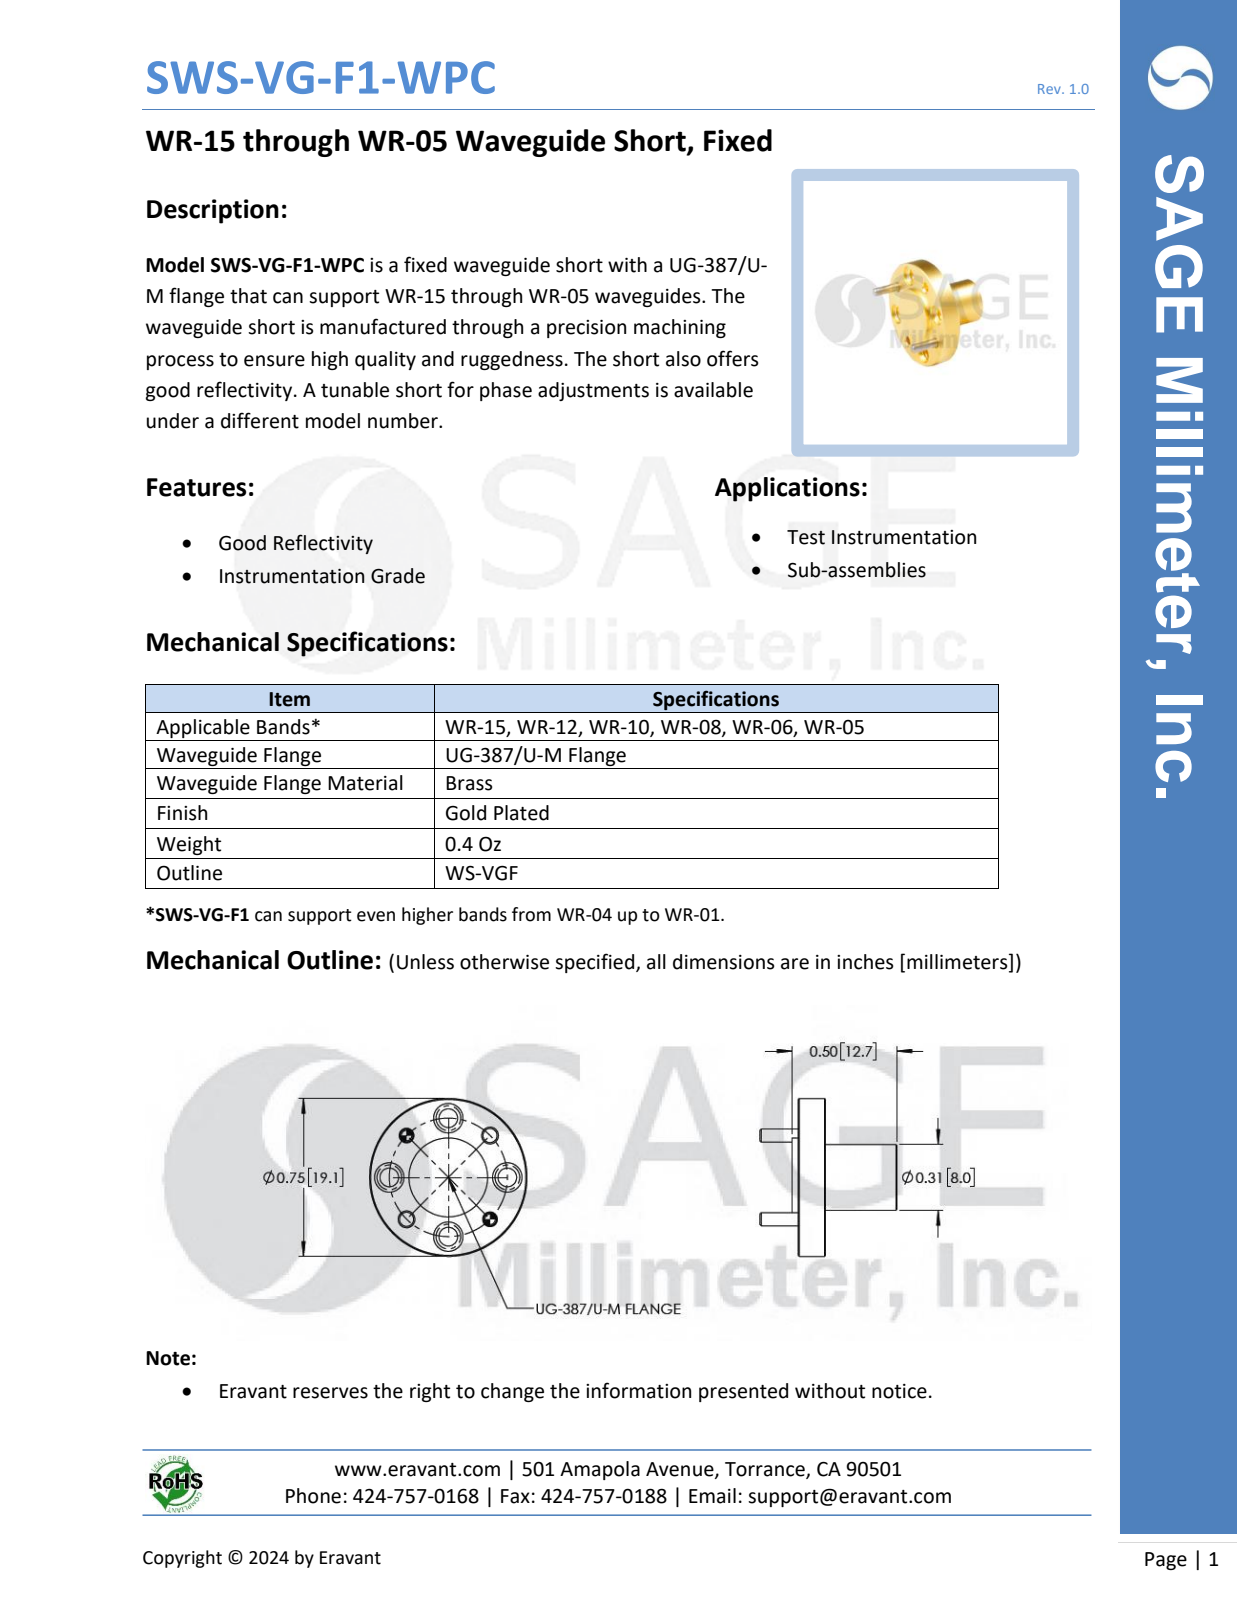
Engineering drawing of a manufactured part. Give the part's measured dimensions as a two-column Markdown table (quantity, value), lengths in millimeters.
| quantity | value |
| --- | --- |
| part name | SWS-VG-F1 |
| STEP written by | SolidWorks 2016 (AUTOMOTIVE_DESIGN) |
| units | millimeters |
| bodies | 3 solids, 68 faces (12 planar, 34 cylindrical, 22 other) |
| overall size | 19.1 × 19.1 × 16.6 |
| volume | 1 400 mm³ |
| surface area | 1 200 mm² |
| round holes (diameter × count) | 2.3 × 4, 3.6 × 4, 1.5 × 2, 1.7 × 2 |
| round bosses / shafts (diameter × count) | 1.6 × 2, 19.1 × 1, 9.5 × 1, 8 × 1 |
| main face-to-face distances | 3.3, 4.1, 0.8, 8.6, 11.9, 12.7, 11.4, 2.8, 0.5, 1.3 |
| hole center spacings | 5.5, 10.1, 13.2, 14.3 |
